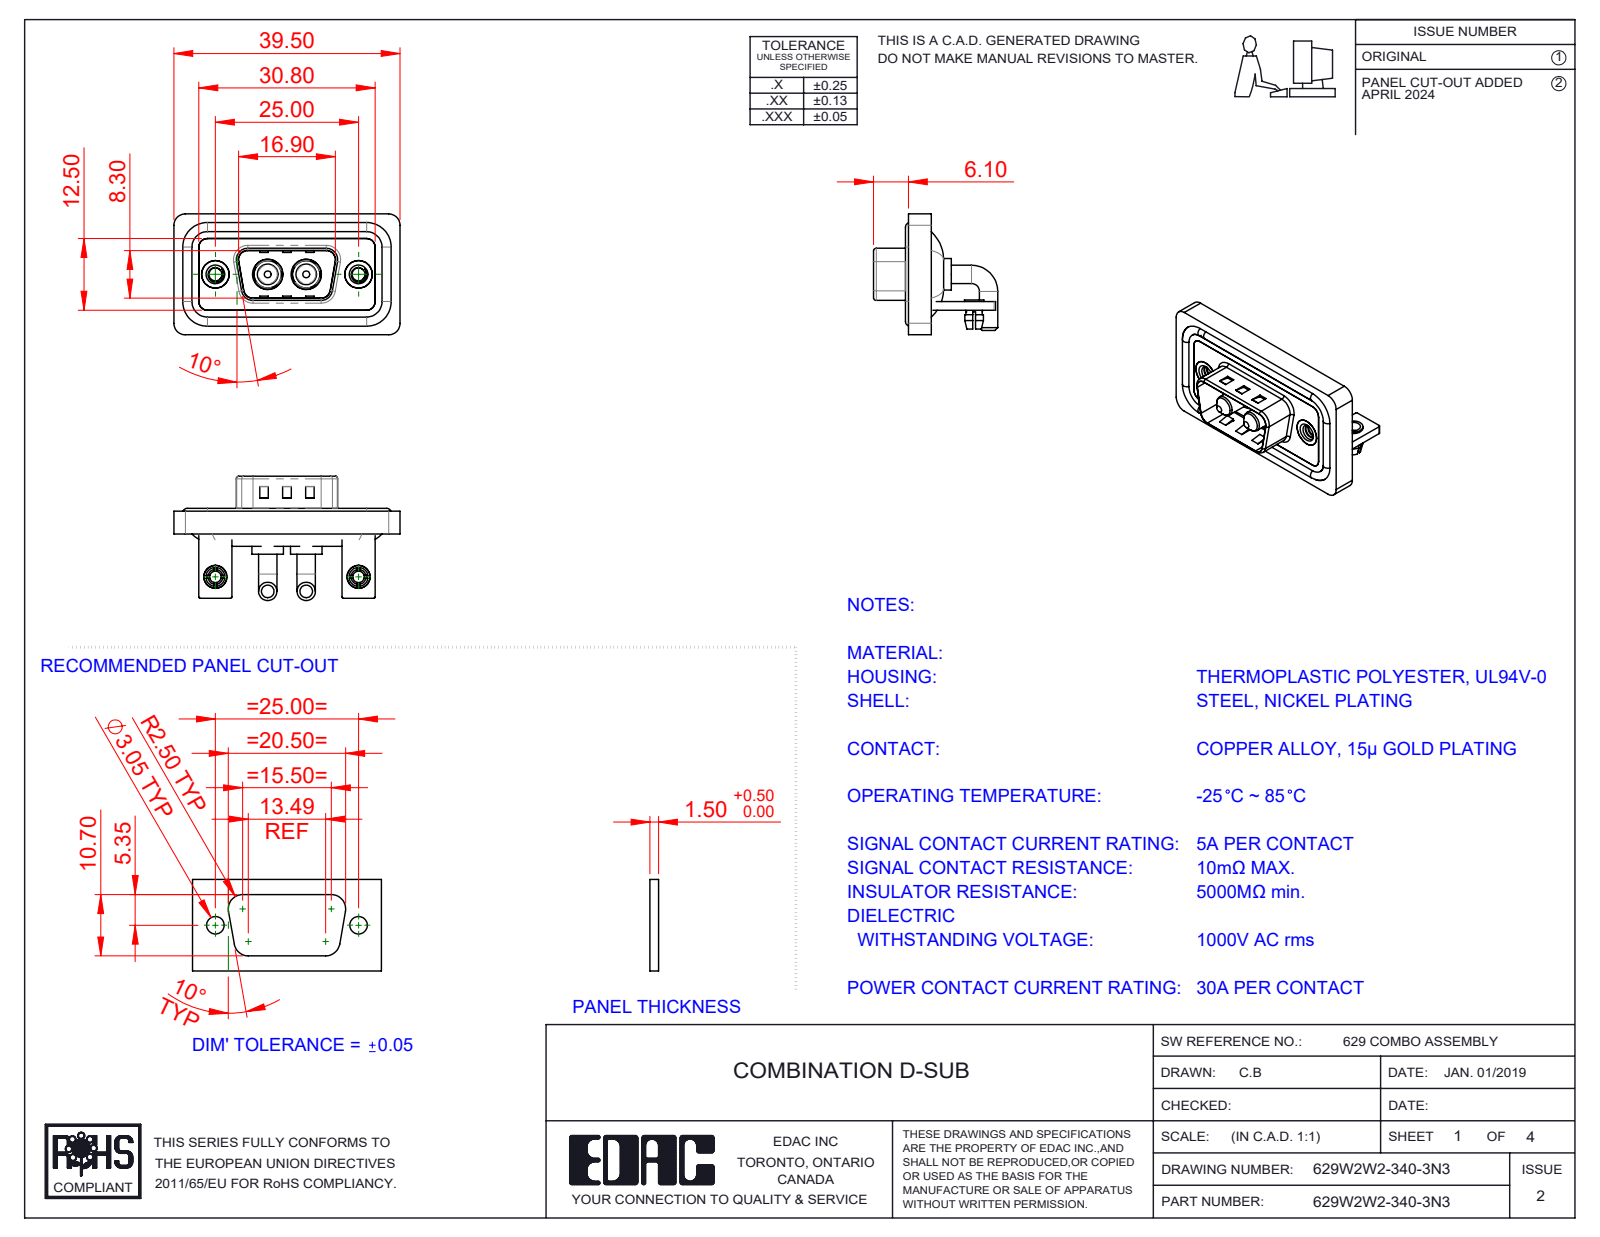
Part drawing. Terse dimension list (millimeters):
name: 629Combo Threaded Rivet_3; Power Pin_30A RA; 629W2W2-340-3N3; 629Combo Housing_2W2 (+5 more)
written by: SolidWorks 2023 (CONFIG_CONTROL_DESIGN)
unit: mm
bodies: 15 solids, 629 faces (233 planar, 272 cylindrical, 124 other)
size: 39.5 × 21.7 × 21.1
volume: 4 954 mm³; area: 8 001 mm²
holes: 2× ⌀2, 2× ⌀2.26, 2× ⌀2.5, 2× ⌀3.2, 2× ⌀4, 2× ⌀4.8, 2× ⌀4.85, 2× ⌀5, 2× ⌀5.3
bosses: 4× ⌀3.2, 4× ⌀1.6, 2× ⌀5.5, 2× ⌀5.2, 2× ⌀4.9, 2× ⌀4.75, 2× ⌀4, 2× ⌀3.75
rounds: 19× R2, 18× R1.5, 16× R0.25, 9× R0.5, 8× R1.6, 4× R0.6, 4× R0.65, 4× R0.9
face distances: 0.4, 1.5, 2.9, 0.8, 1.1, 1.2, 2.1, 1.6, 3.7, 2.5
hole spacings: 9.14, 15.86, 25, 6.72
